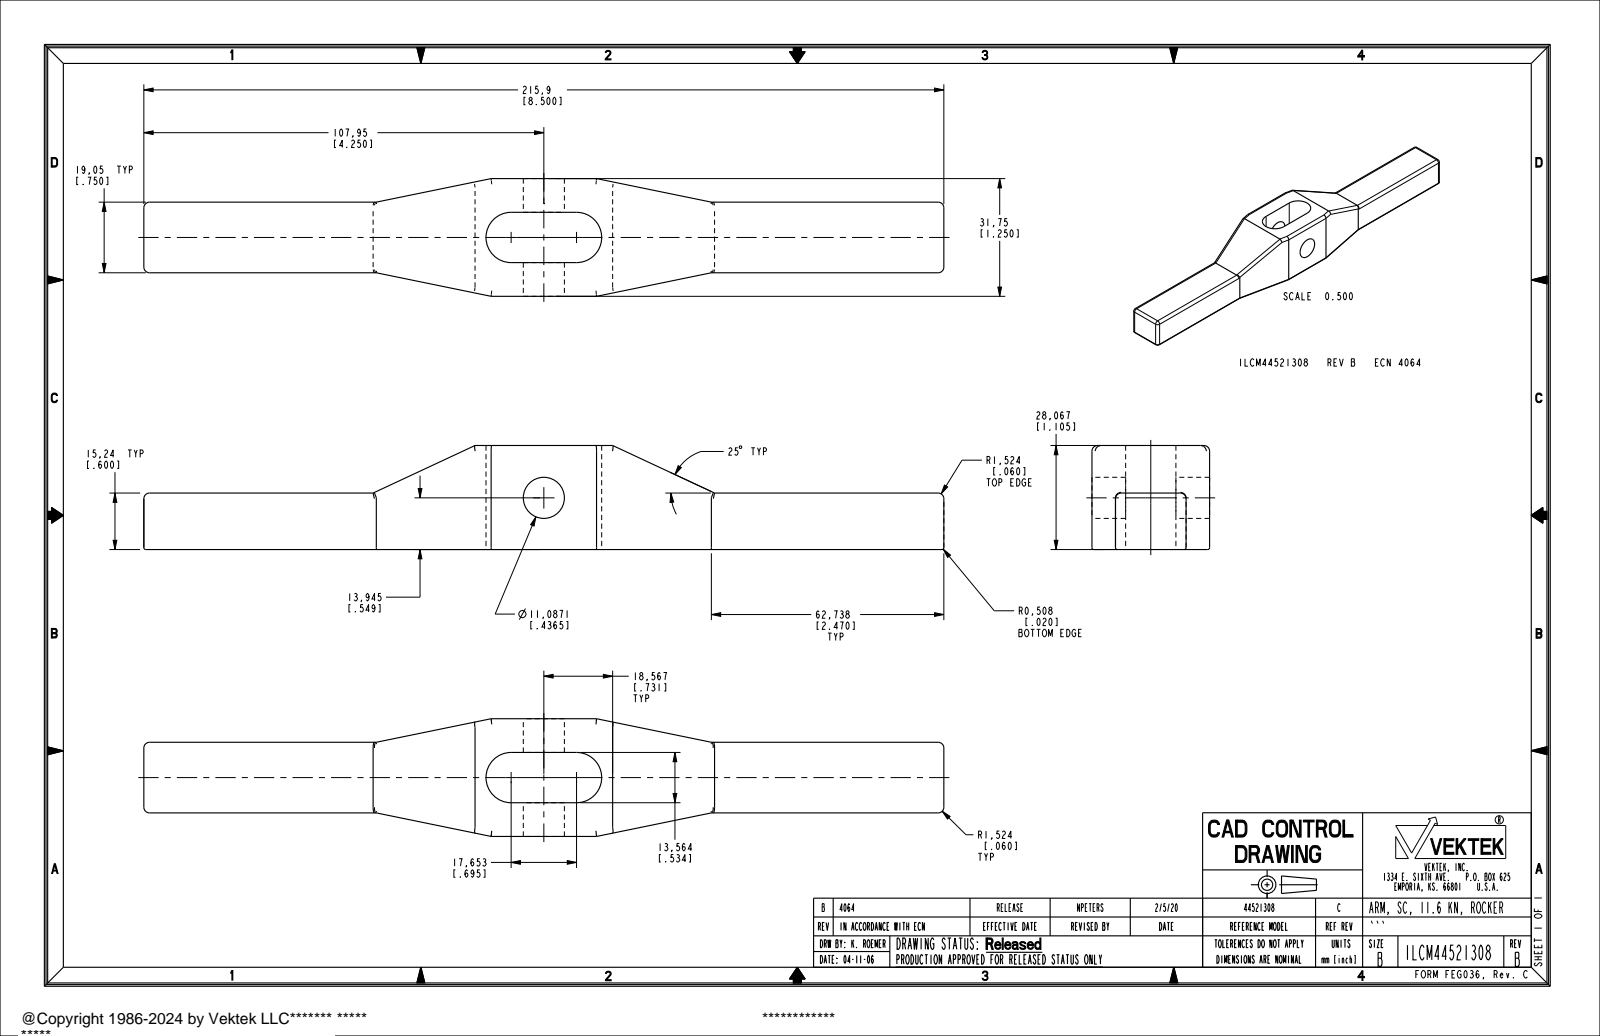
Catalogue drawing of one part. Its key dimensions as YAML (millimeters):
part_name: "ILCM44521308"
step_written_by: "PRO/ENGINEER BY PARAMETRIC TECHNOLOGY CORPORATION, 2013320 (AUTOMOTIVE_DESIGN)"
units: millimeters
bodies: {solids: 1, faces: 70, planar: 20, cylindrical: 42, other: 8}
overall_size: [215.9, 31.75, 28.07]
volume: 85641
surface_area: 19971
round_holes:
  - {diameter: 11.09, count: 1}
partial_cylinders:
  - {radius: 1.52, count: 22}
  - {radius: 0.51, count: 10}
  - {radius: 6.78, count: 2}
face_to_face_distances: [15.24, 19.06, 6.35, 25.41, 9.1, 22.66, 2.75, 16.31, 28.07, 12.83]
